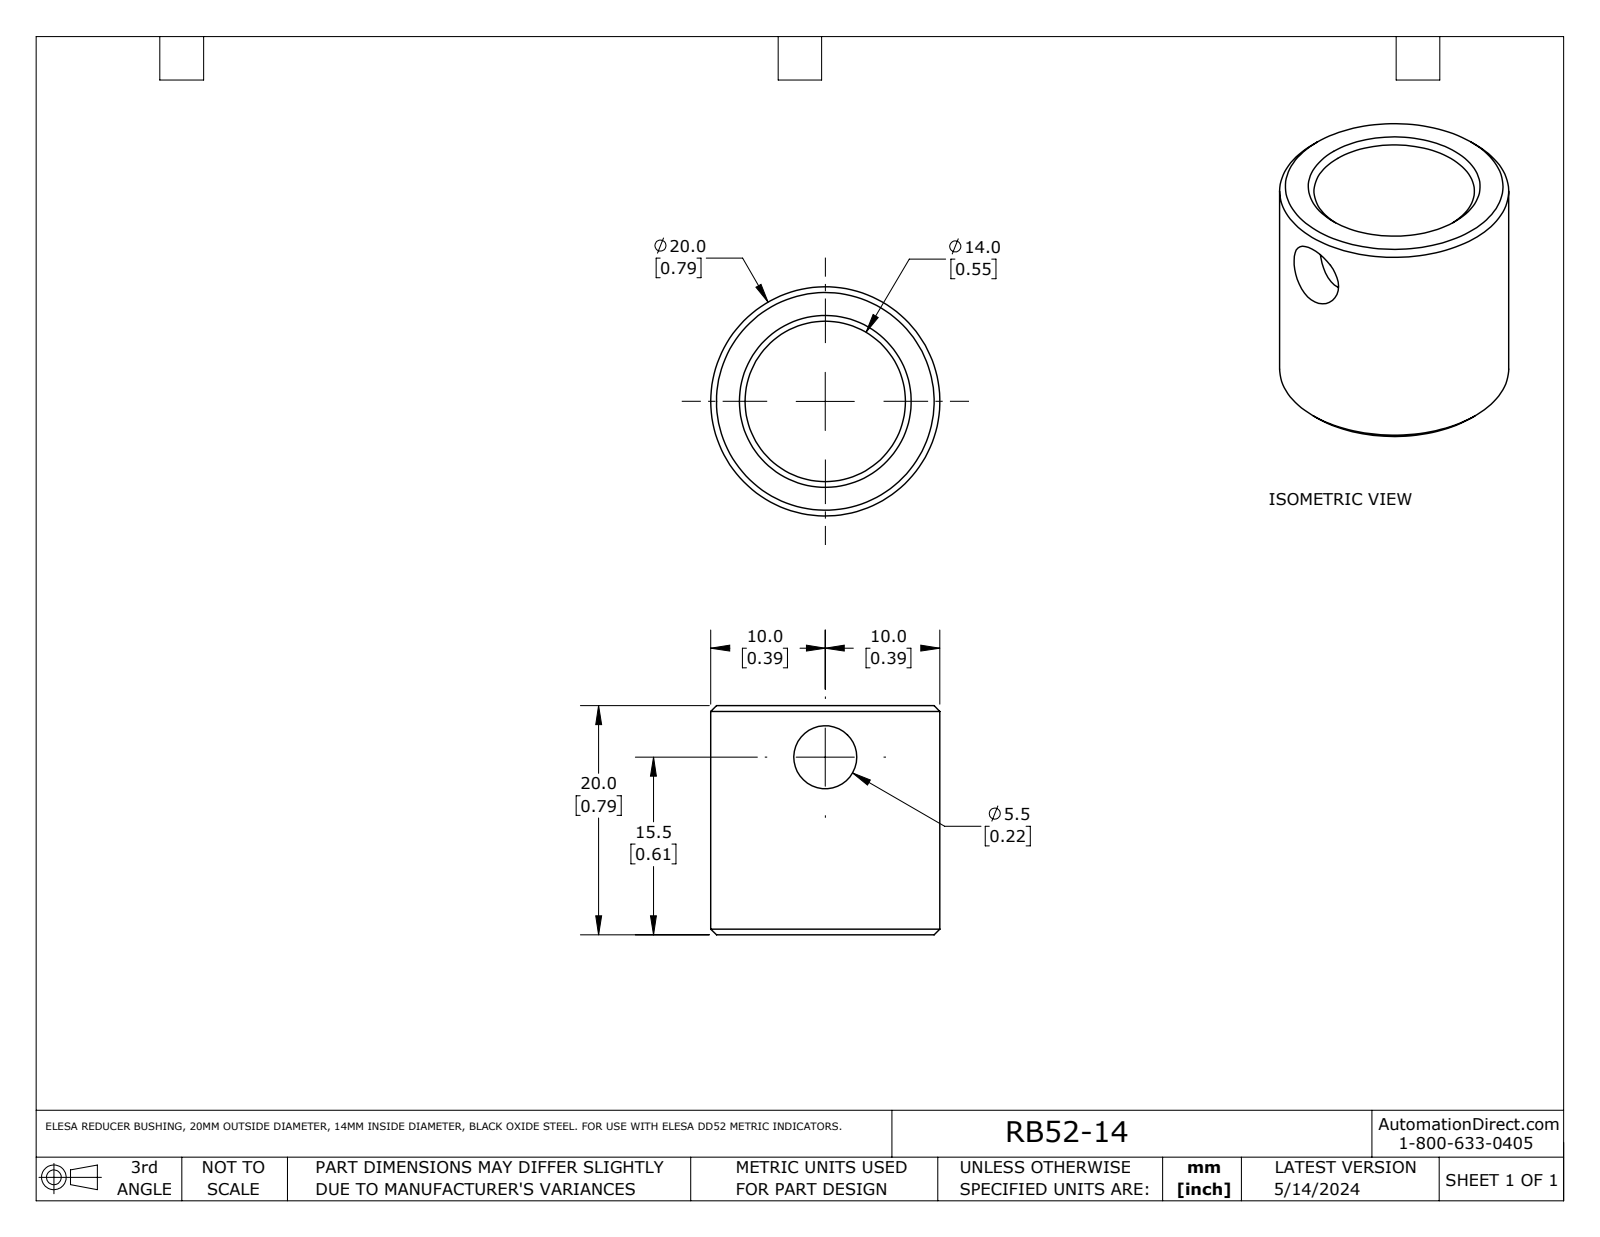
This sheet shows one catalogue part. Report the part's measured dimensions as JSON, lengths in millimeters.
{"part_name": "RB52-14", "step_written_by": "SolidWorks 2023 (AUTOMOTIVE_DESIGN)", "units": "millimeters", "bodies": {"solids": 1, "faces": 9, "planar": 2, "cylindrical": 3, "other": 4}, "overall_size": [20, 20, 20], "volume_mm3": 3100, "surface_area_mm2": 2399, "round_holes": [[5.5, 1], [14, 1]], "round_bosses_or_shafts": [[20, 1]], "face_to_face_distances": [20]}
